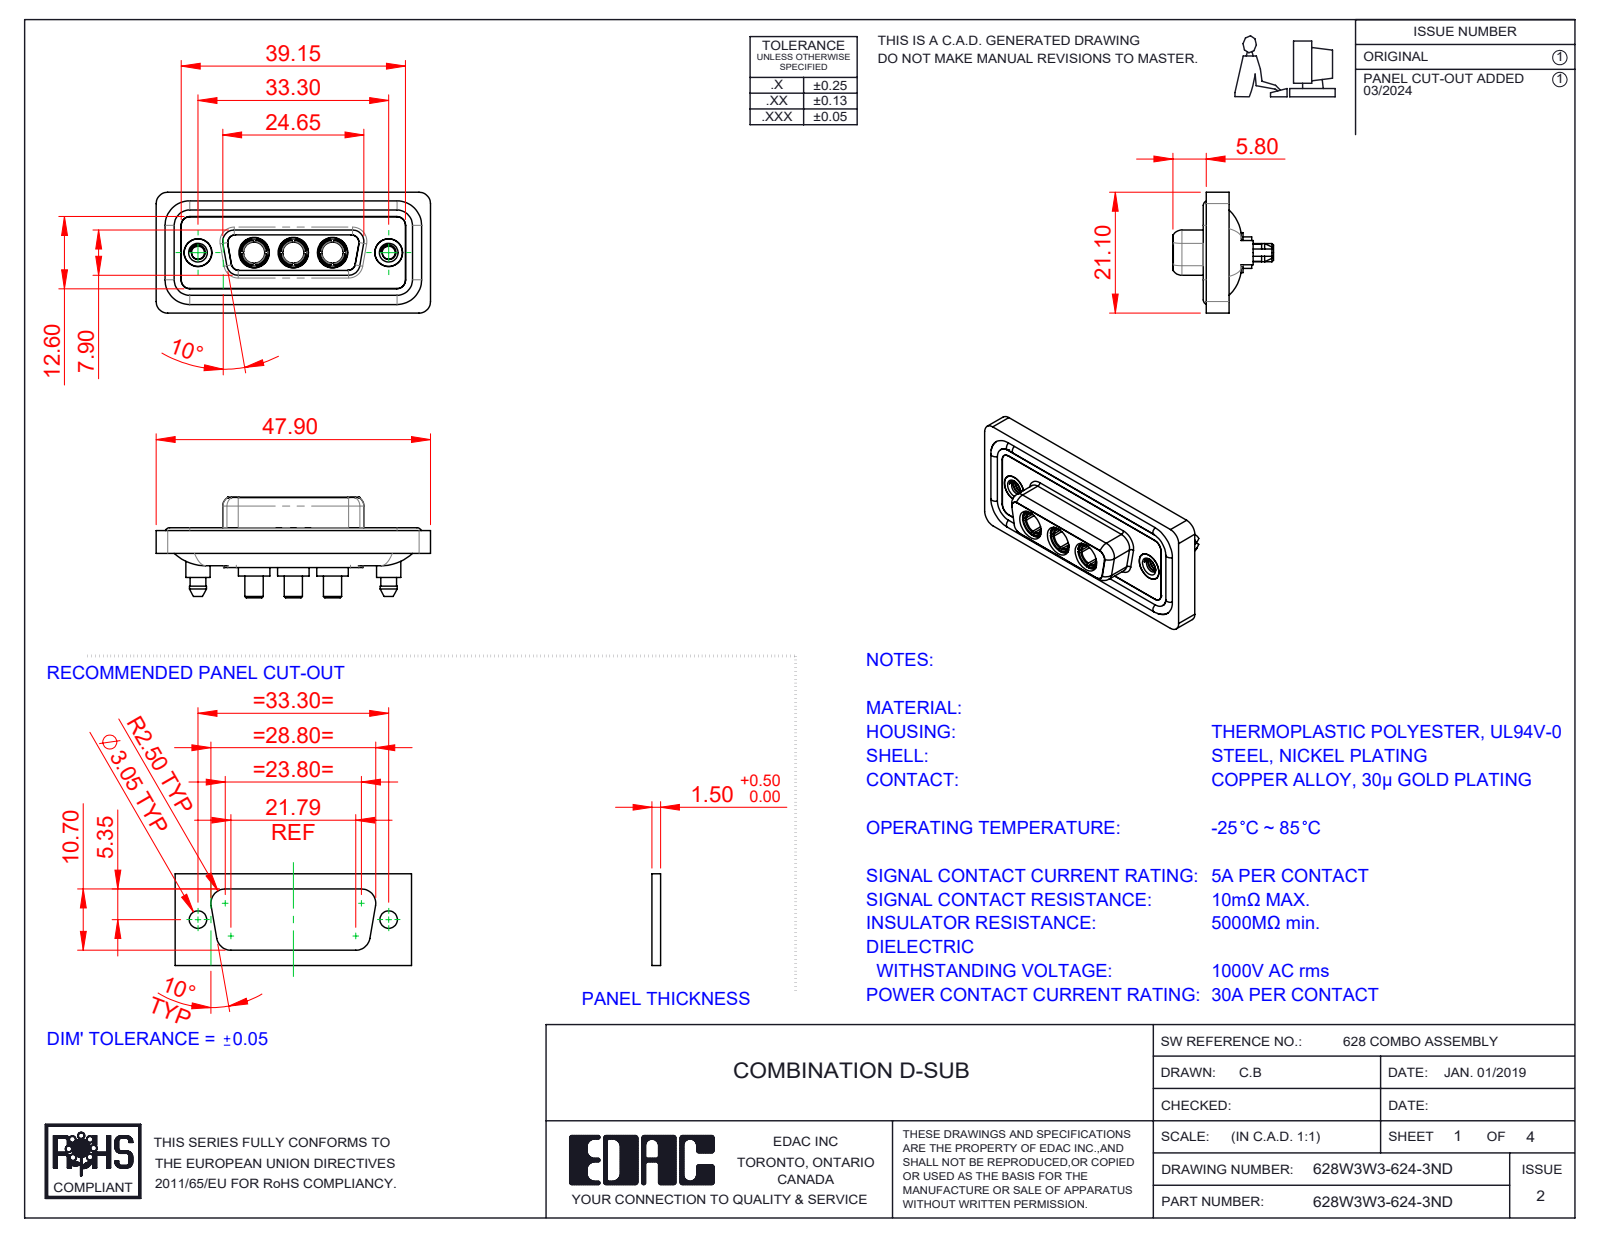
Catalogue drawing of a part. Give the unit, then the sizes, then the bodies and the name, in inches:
Units: inches
Overall size (bounding box): 1.886 × 0.831 × 0.691
Round holes (diameter × count): ⌀0.191 ×5, ⌀0.146 ×3, ⌀0.209 ×3, ⌀0.089 ×2, ⌀0.157 ×2, ⌀0.159 ×2, ⌀0.197 ×2
Round bosses / shafts (diameter × count): ⌀0.063 ×4, ⌀0.217 ×3, ⌀0.205 ×3, ⌀0.195 ×3, ⌀0.187 ×3, ⌀0.148 ×3, ⌀0.126 ×3, ⌀0.213 ×2
Partial cylindrical surfaces — rounded edges, fillets, slot ends (radius × count): R0.059 ×24, R0.079 ×20, R0.053 ×12, R0.063 ×10, R0.01 ×4, R0.02 ×4, R0.024 ×4, R0.026 ×4
Main face-to-face distances: 0.016, 0.071, 0.063, 0.02, 0.293, 0.043, 0.114, 0.222, 0.278, 0.26
Hole centre spacings: 0.27, 0.386, 0.656, 0.925, 0.539, 1.311
Volume: 0.377 in³ · Surface area: 15.64 in²
Bodies: 13 solids, 674 faces (208 planar, 305 cylindrical, 161 other)
Part name (STEP PRODUCT): 628W3W3-624-3ND; 628Combo Housing_3W3; 628Combo Waterproof Housing_15 Contacts; 628Combo Threaded Boardlock_D (+3 more)
STEP written by: SolidWorks 2023 (CONFIG_CONTROL_DESIGN)
